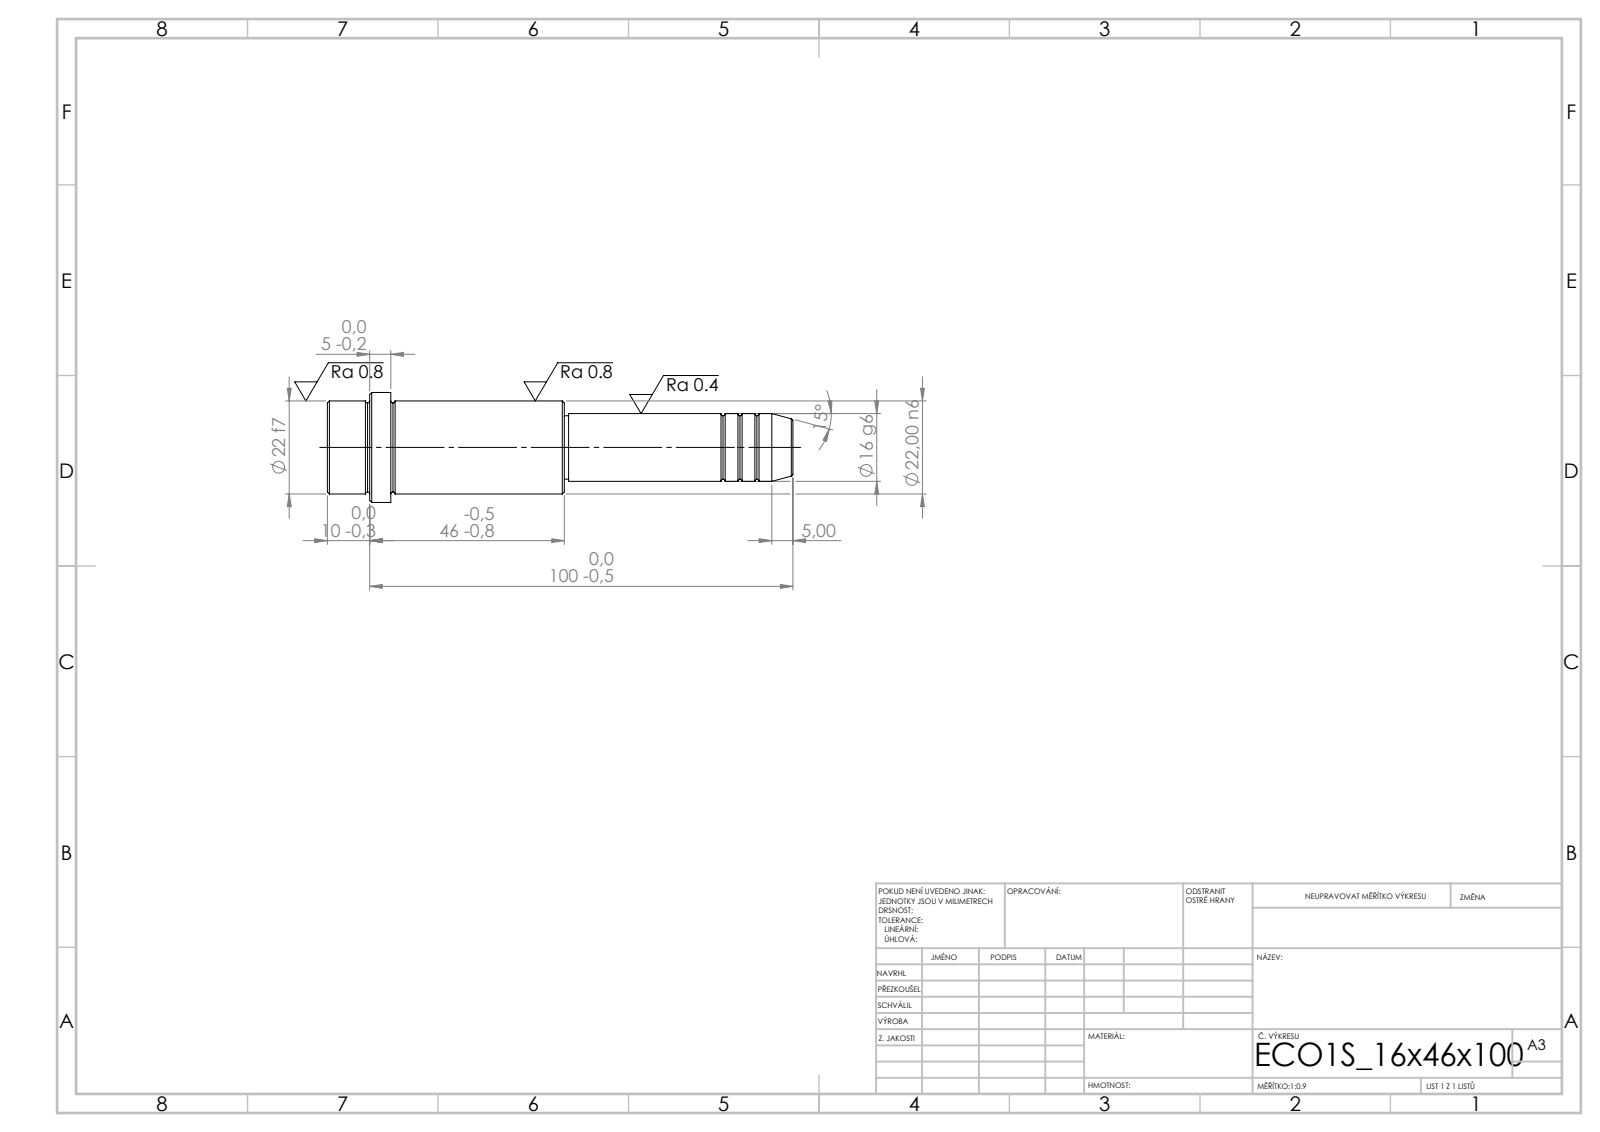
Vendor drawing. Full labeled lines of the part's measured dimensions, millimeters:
STEP written by: SolidWorks 2019 (CONFIG_CONTROL_DESIGN)
Units: millimetres
Bodies: 1 solid, 52 faces (6 planar, 16 cylindrical, 30 other)
Overall size (bounding box): 110 × 26 × 26
Volume: 32 576 mm³ · Surface area: 7 759 mm²
Round bosses / shafts (diameter × count): ⌀26 ×1, ⌀22 ×1, ⌀16 ×1, ⌀15 ×1
Main face-to-face distances: 56, 41, 15, 54, 95, 110, 100, 46, 5, 10
